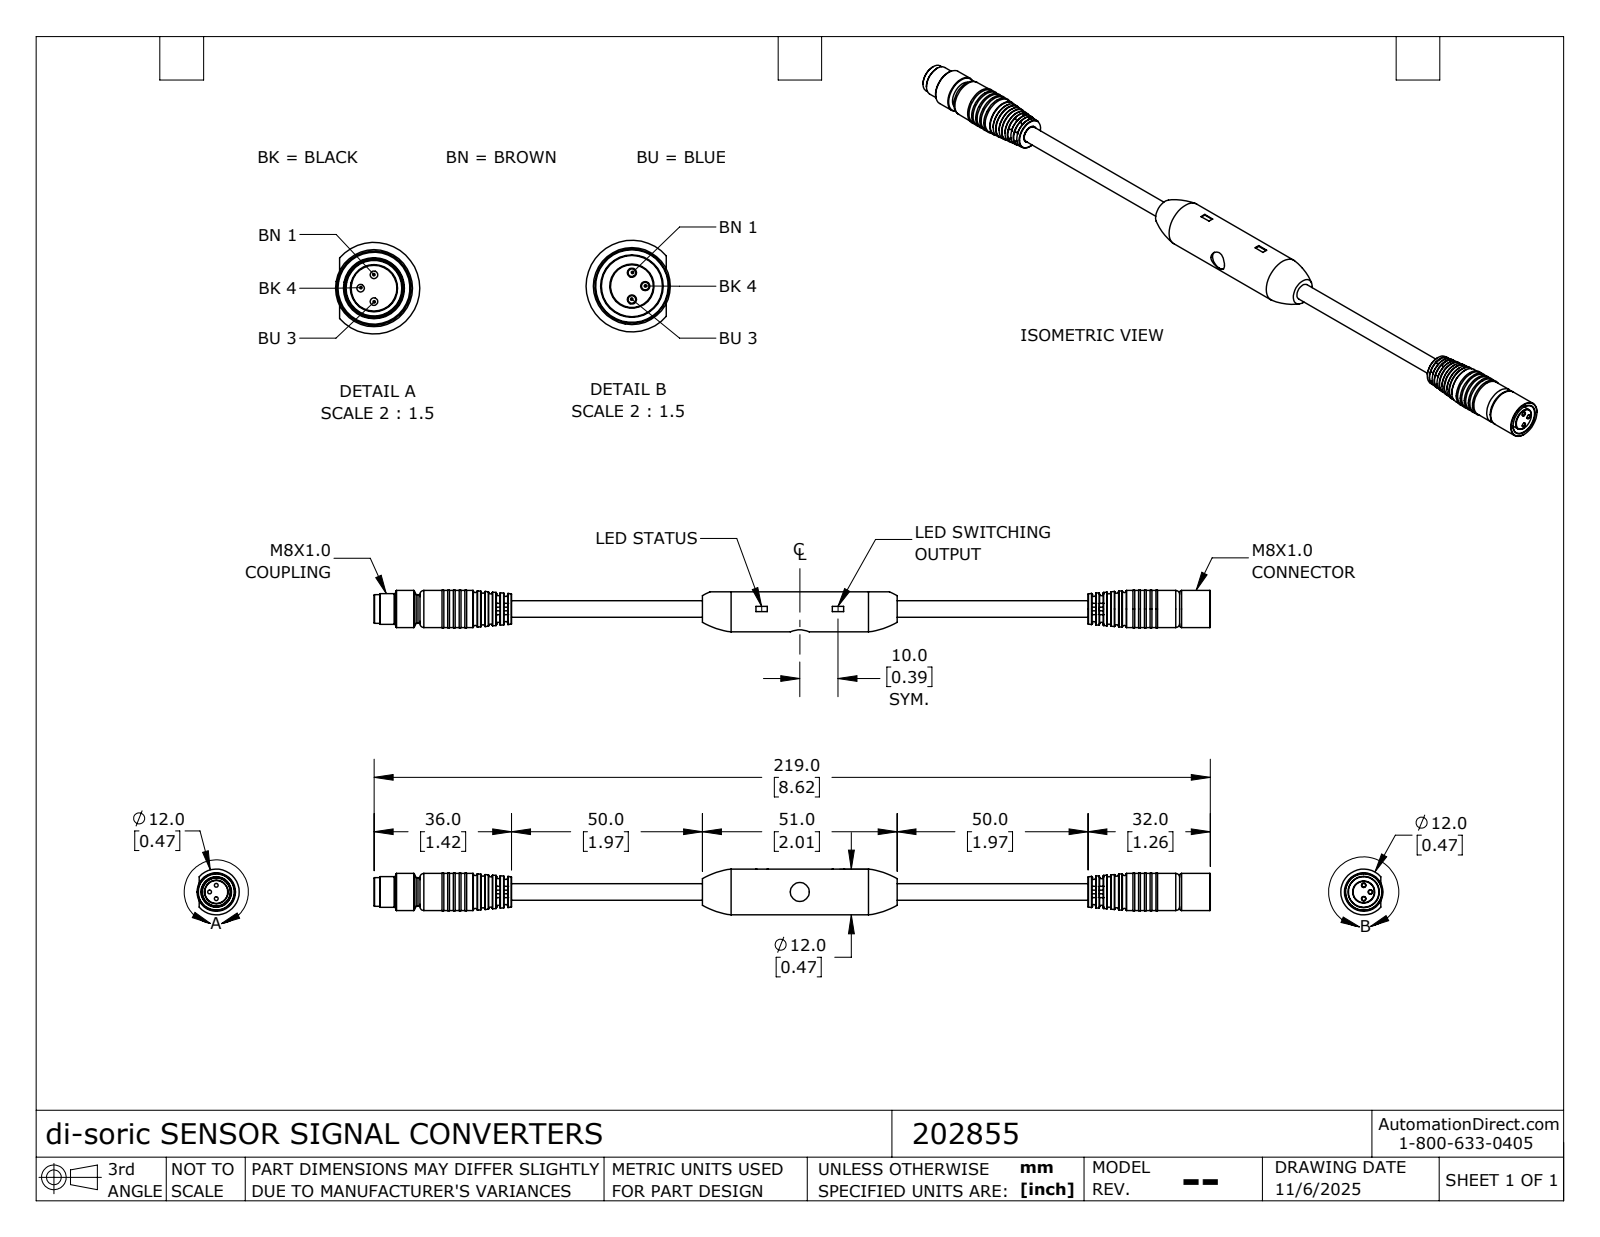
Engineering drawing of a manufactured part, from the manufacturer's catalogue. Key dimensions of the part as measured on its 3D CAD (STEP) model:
Part name (STEP PRODUCT): TKHM-Z_TSM-Z_P4
STEP written by: SolidWorks 2024 (AUTOMOTIVE_DESIGN)
Units: millimetres
Bodies: 1 solid, 260 faces (132 planar, 42 cylindrical, 86 other)
Overall size (bounding box): 219 × 12 × 12
Volume: 10 010 mm³ · Surface area: 7 758 mm²
Round holes (diameter × count): ⌀1 ×3, ⌀1.43 ×3, ⌀1.72 ×3, ⌀3 ×1, ⌀4.6 ×1, ⌀5 ×1, ⌀6 ×1, ⌀8 ×1
Round bosses / shafts (diameter × count): ⌀9.7 ×1, ⌀7.9 ×1, ⌀7.5 ×1, ⌀5.8 ×1, ⌀4.5 ×1, ⌀4.3 ×1
Partial cylindrical surfaces — rounded edges, fillets, slot ends (radius × count): R6 ×1
Main face-to-face distances: 1, 2, 3, 155, 154, 156, 51, 157, 153, 6
Hole centre spacings: 1.6, 0.84, 1, 1.46, 1.75, 1.01, 1.1, 1.73
